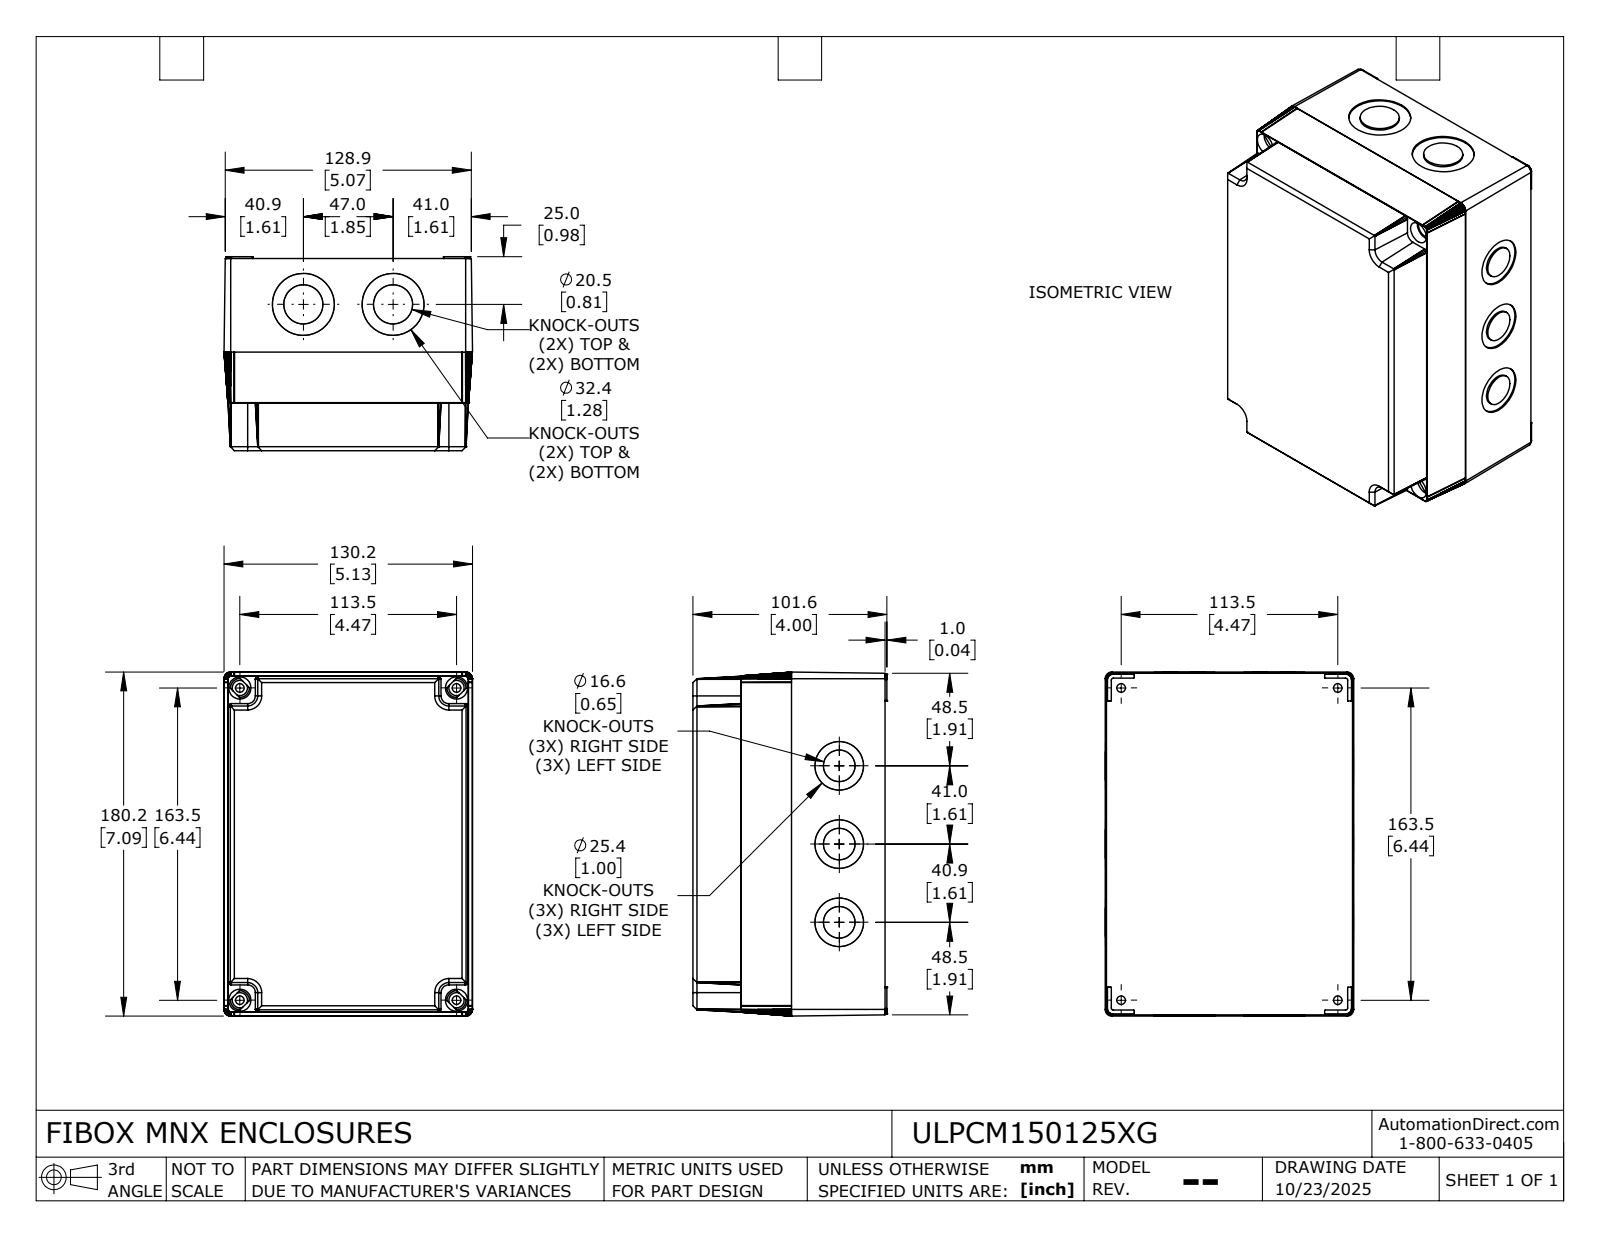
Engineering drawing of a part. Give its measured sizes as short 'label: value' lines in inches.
name: ULPCM20088XG
written by: SolidWorks 2024 (AUTOMOTIVE_DESIGN)
unit: in
bodies: 2 solids, 1665 faces (1517 planar, 60 cylindrical, 88 other)
size: 7.094 × 5.125 × 4
volume: 19.94 in³; area: 337.4 in²
holes: 4× ⌀0.177, 4× ⌀0.315, 4× ⌀0.456
rounds: 8× R0.158, 8× R0.191, 4× R0.01, 4× R0.043, 4× R0.075, 4× R0.114, 4× R0.195, 4× R0.201
face distances: 0.136, 0.118, 3.961, 3.843, 0.079, 3.882, 3.764, 0.096, 1.929, 1.811
hole spacings: 4.469, 6.437, 7.836
